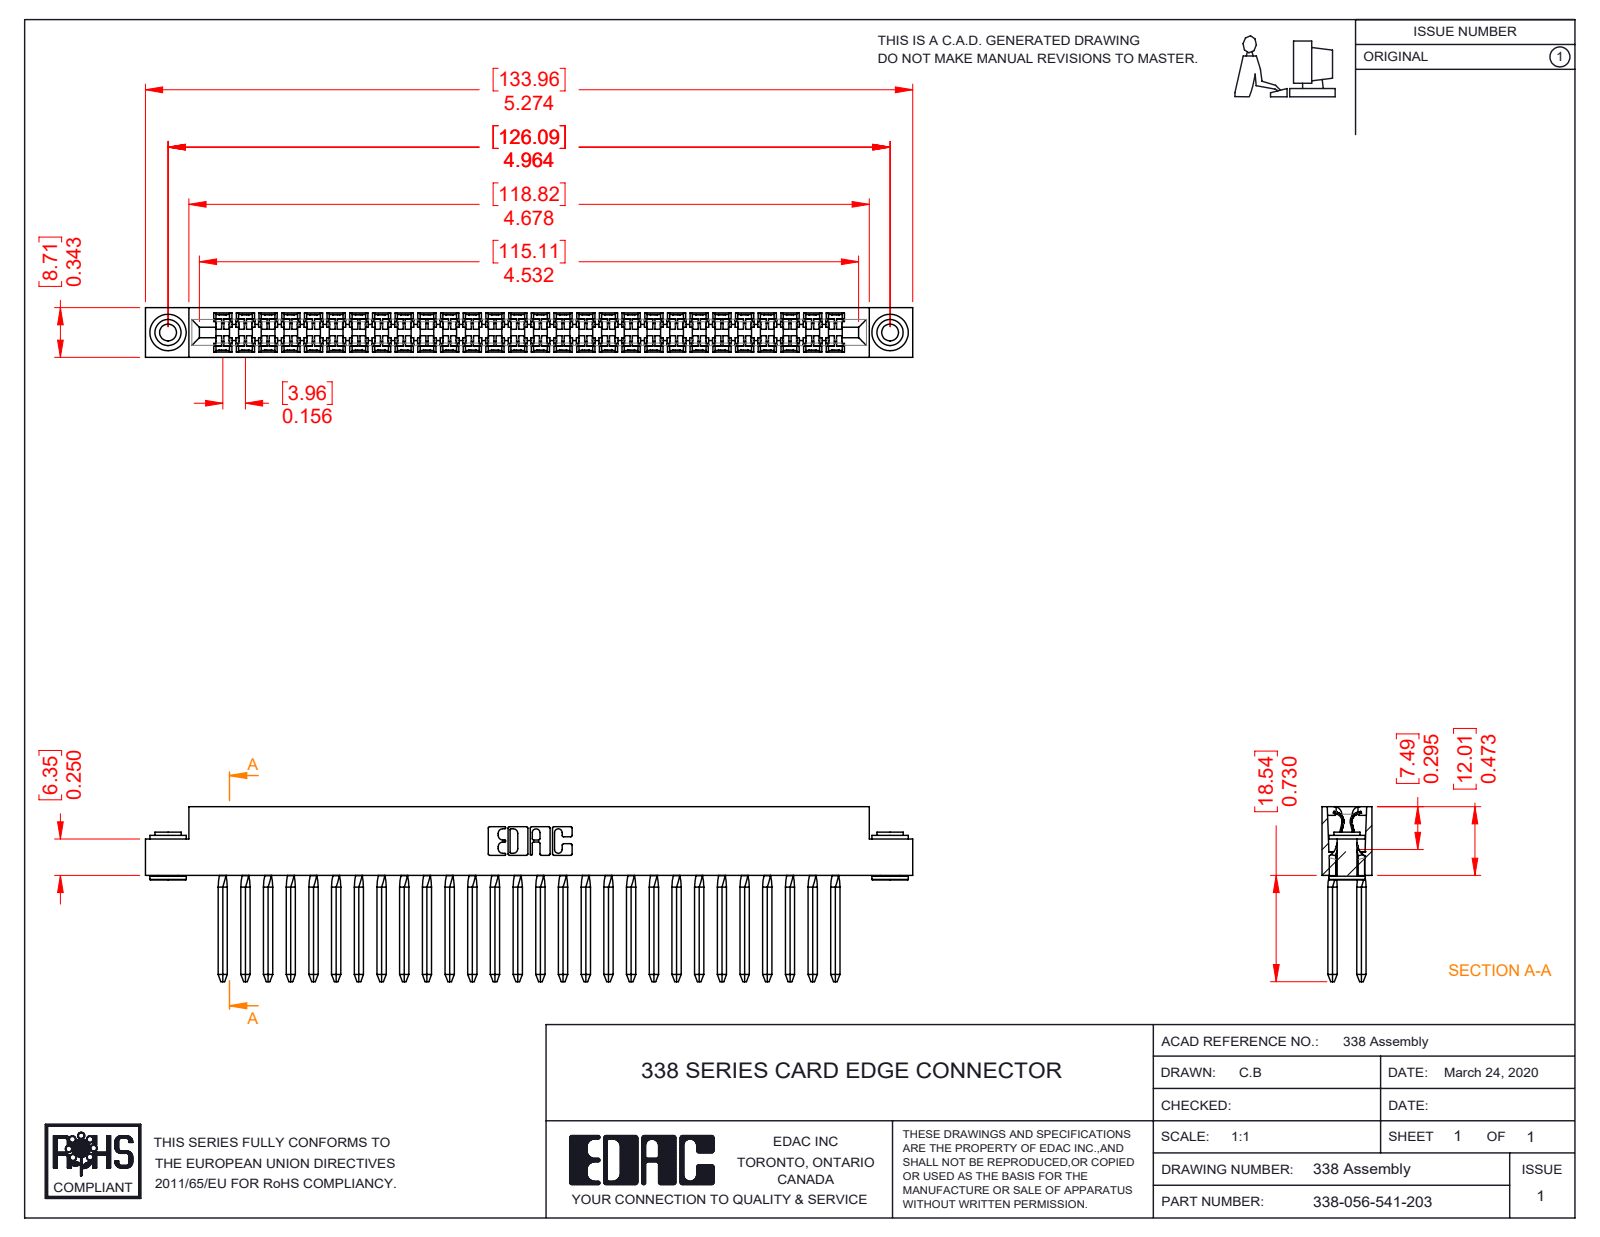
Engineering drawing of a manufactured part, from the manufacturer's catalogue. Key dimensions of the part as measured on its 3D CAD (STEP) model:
Part name (STEP PRODUCT): 345-250-002_345-250-002-102; 338-290-001_541; 338-056-541-203; 338-210-001_338-210-028-004
STEP written by: SolidWorks 2016 (CONFIG_CONTROL_DESIGN)
Units: inches
Bodies: 59 solids, 3898 faces (2706 planar, 960 cylindrical, 232 other)
Overall size (bounding box): 5.274 × 1.203 × 0.343
Volume: 0.632 in³ · Surface area: 30.63 in²
Round holes (diameter × count): ⌀0.116 ×2, ⌀0.156 ×2
Round bosses / shafts (diameter × count): ⌀0.25 ×2, ⌀0.18 ×2, ⌀0.136 ×2
Partial cylindrical surfaces — rounded edges, fillets, slot ends (radius × count): R0.025 ×170, R0.008 ×56, R0.055 ×46, R0.067 ×46, R0.1 ×44, R0.01 ×22, R0.007 ×6, R0.031 ×6
Main face-to-face distances: 0.343, 0.156, 0.11, 0.207, 0.135, 0.624, 0.16, 0.78, 0.468, 0.072
Hole centre spacings: 4.964
